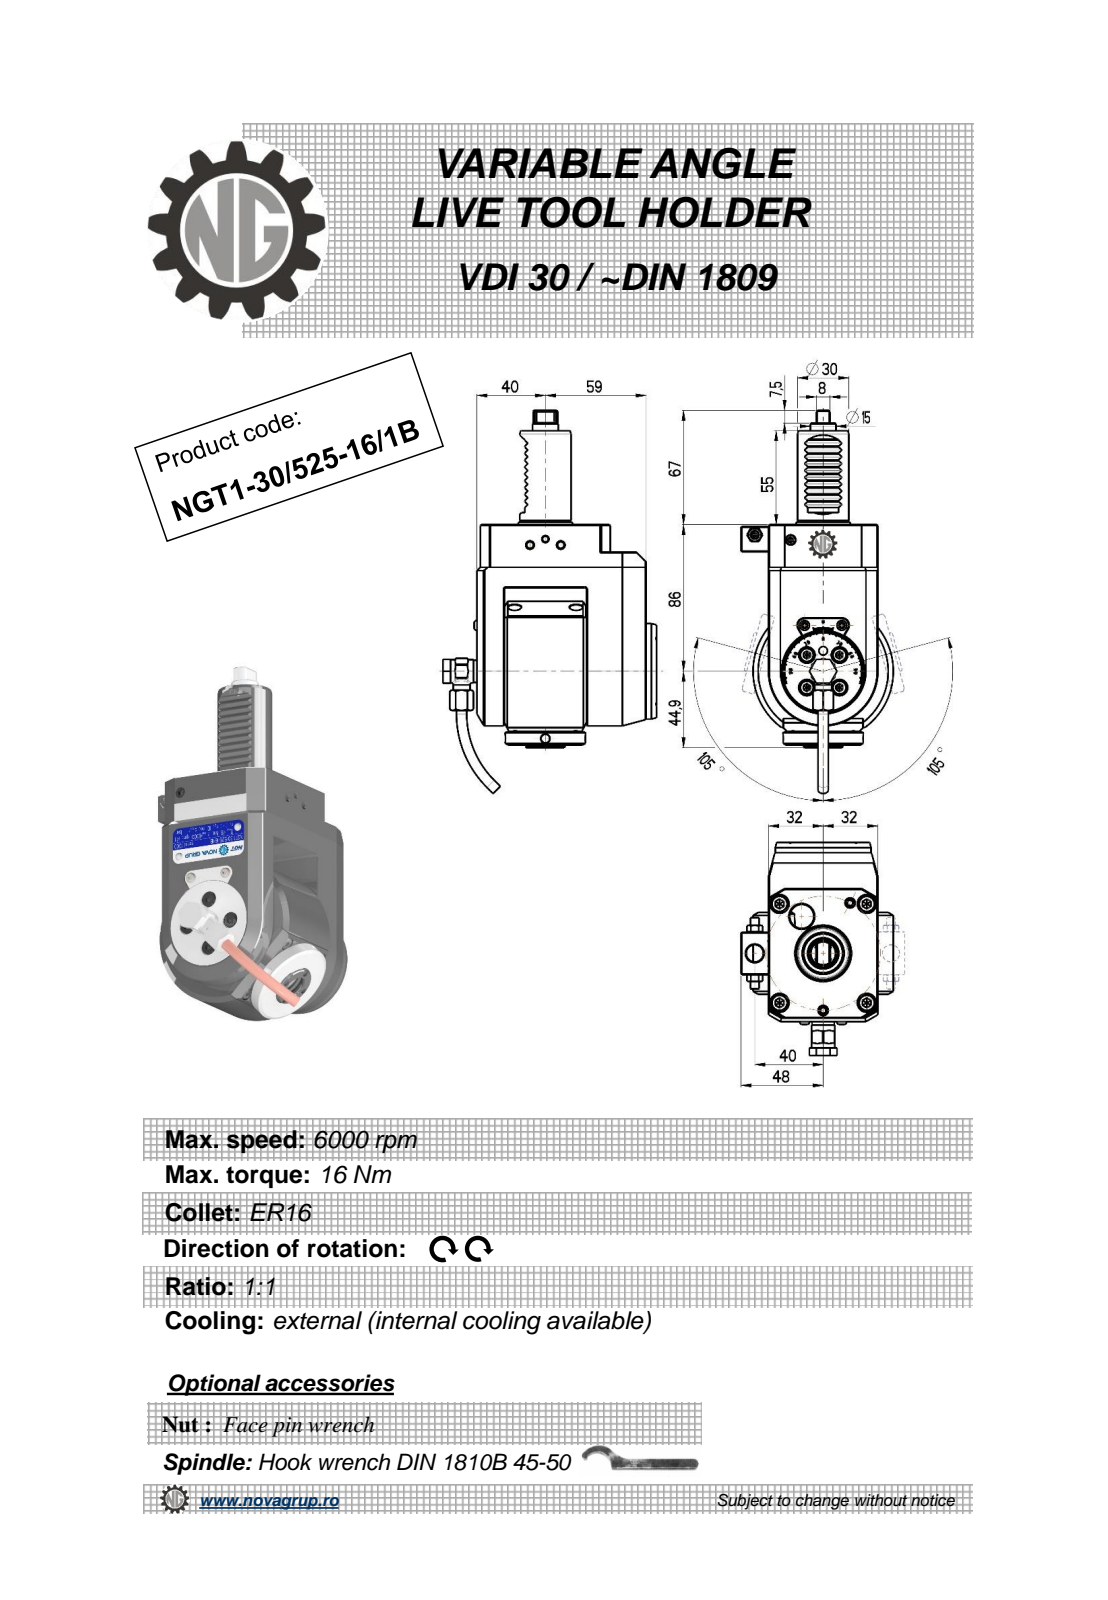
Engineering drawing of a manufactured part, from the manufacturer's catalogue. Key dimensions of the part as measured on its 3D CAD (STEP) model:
Part name (STEP PRODUCT): NGT1_30_521_16_1B
STEP written by: PRO/ENGINEER BY PARAMETRIC TECHNOLOGY CORPORATION, 2010280 (CONFIG_CONTROL_DESIGN)
Units: millimetres
Bodies: 1 solid, 502 faces (212 planar, 138 cylindrical, 152 other)
Overall size (bounding box): 224.67 × 124.9 × 89
Volume: 760 250 mm³ · Surface area: 71 546 mm²
Round holes (diameter × count): ⌀3.2 ×4, ⌀4 ×3, ⌀5 ×2, ⌀3 ×1, ⌀4.2 ×1, ⌀6.2 ×1, ⌀9 ×1, ⌀9.5 ×1, ⌀10 ×1, ⌀11 ×1, ⌀12.5 ×1
Round bosses / shafts (diameter × count): ⌀10 ×2, ⌀6 ×2, ⌀5.7 ×2, ⌀82 ×1, ⌀56 ×1, ⌀47 ×1, ⌀35 ×1, ⌀30 ×1
Partial cylindrical surfaces — rounded edges, fillets, slot ends (radius × count): R0.26 ×12, R0.3 ×10, R0.16 ×6, R0.5 ×4, R0.8 ×2, R1 ×2, R7.2 ×1, R7.7 ×1
Main face-to-face distances: 64, 16, 37, 99, 6, 105, 83, 21, 14, 35
Hole centre spacings: 9.25, 13.08, 18.5, 41.06, 49.87, 50.26, 0.4, 30.75
